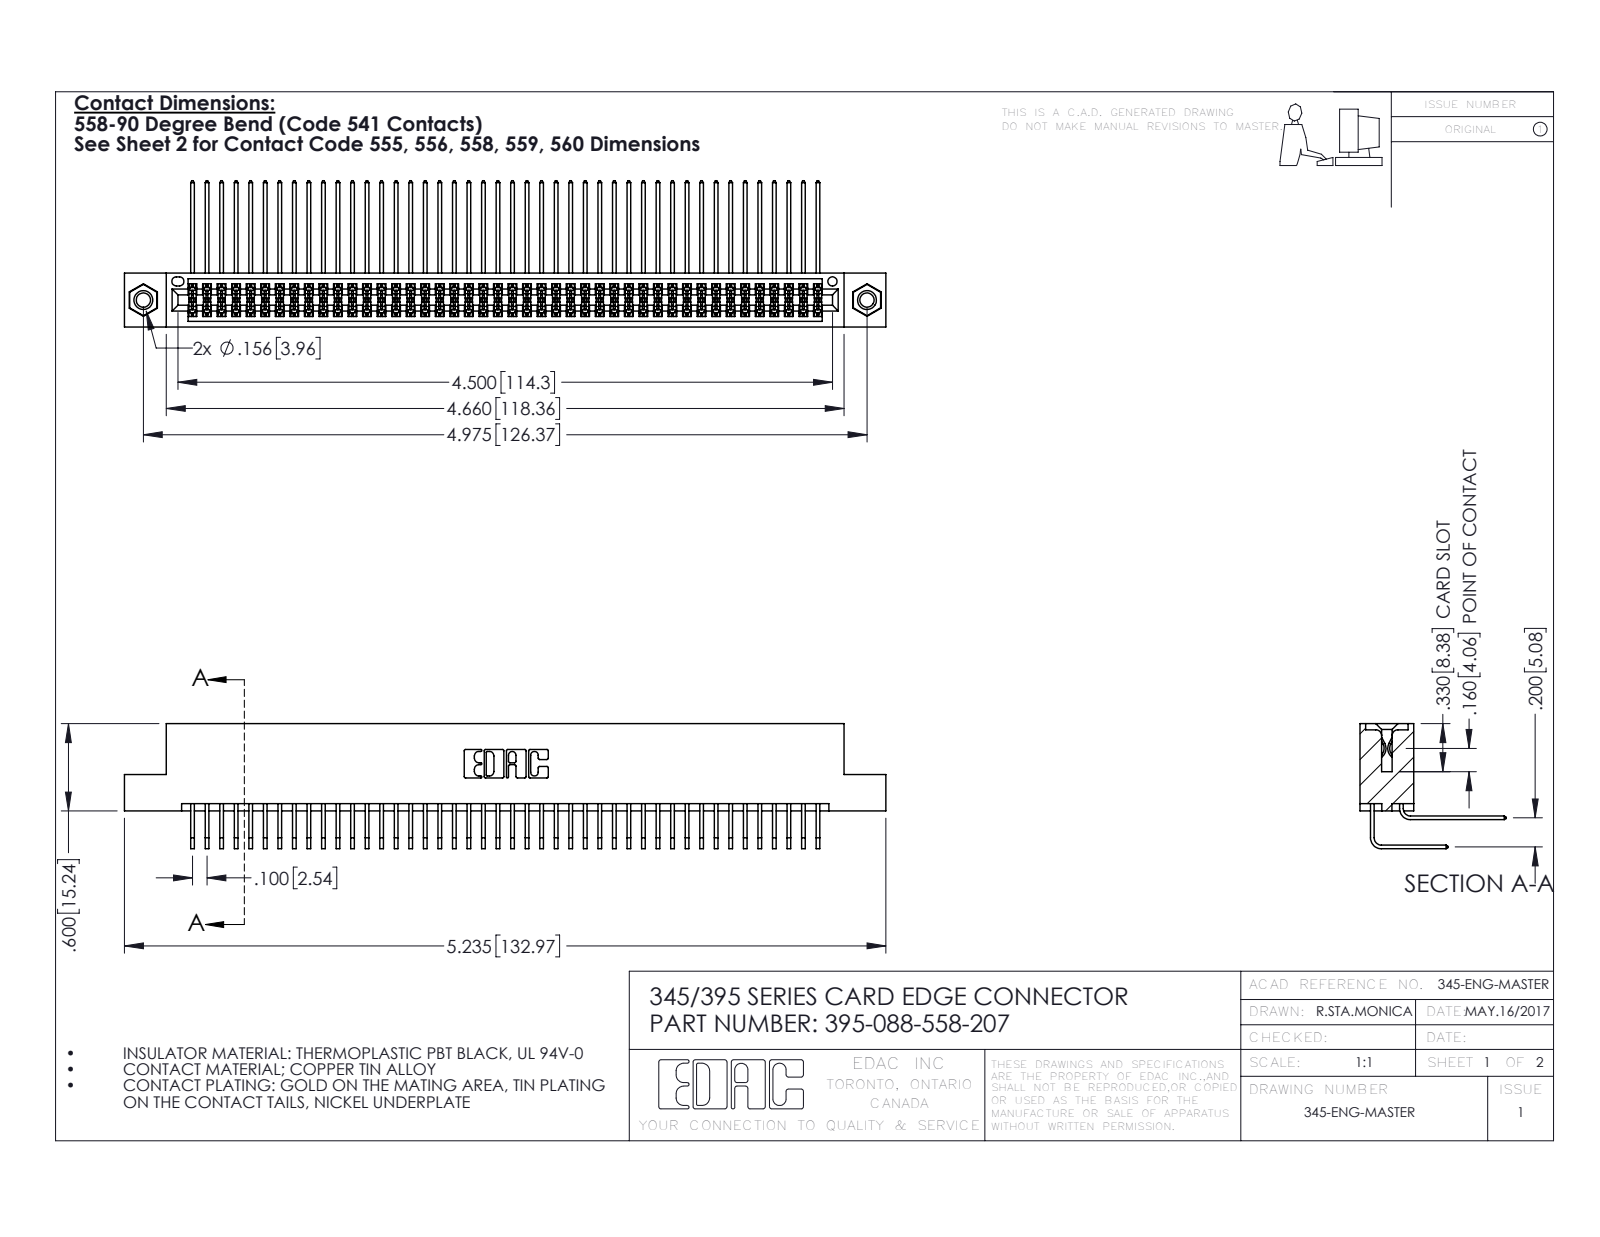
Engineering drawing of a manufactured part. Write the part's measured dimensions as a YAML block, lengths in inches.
part_name: "395-088-558-207; 345-250-001_345-250-005-103; 345 Part_Flush Mounting Lugs - 0.156 Dia-TI; 345-292-001_558 Tail - 2 (+1 more)"
step_written_by: "SolidWorks 2016 (CONFIG_CONTROL_DESIGN)"
units: inches
bodies: {solids: 91, faces: 4762, planar: 3192, cylindrical: 1554, other: 16}
overall_size: [5.235, 1.005, 0.859]
volume: 0.82
surface_area: 34.57
round_holes:
  - {diameter: 0.098, count: 2}
  - {diameter: 0.125, count: 2}
  - {diameter: 0.156, count: 2}
  - {diameter: 0.064, count: 1}
round_bosses_or_shafts:
  - {diameter: 0.155, count: 2}
partial_cylinders:
  - {radius: 0.006, count: 133}
  - {radius: 0.01, count: 22}
  - {radius: 0.007, count: 6}
  - {radius: 0.031, count: 6}
  - {radius: 0.026, count: 3}
  - {radius: 0.014, count: 2}
  - {radius: 0.019, count: 2}
  - {radius: 0.022, count: 2}
face_to_face_distances: [0.072, 0.298, 0.2, 0.37, 0.098, 0.272, 0.025, 0.225, 0.025, 0.175]
hole_center_spacings: [0.27, 4.739, 4.975]
